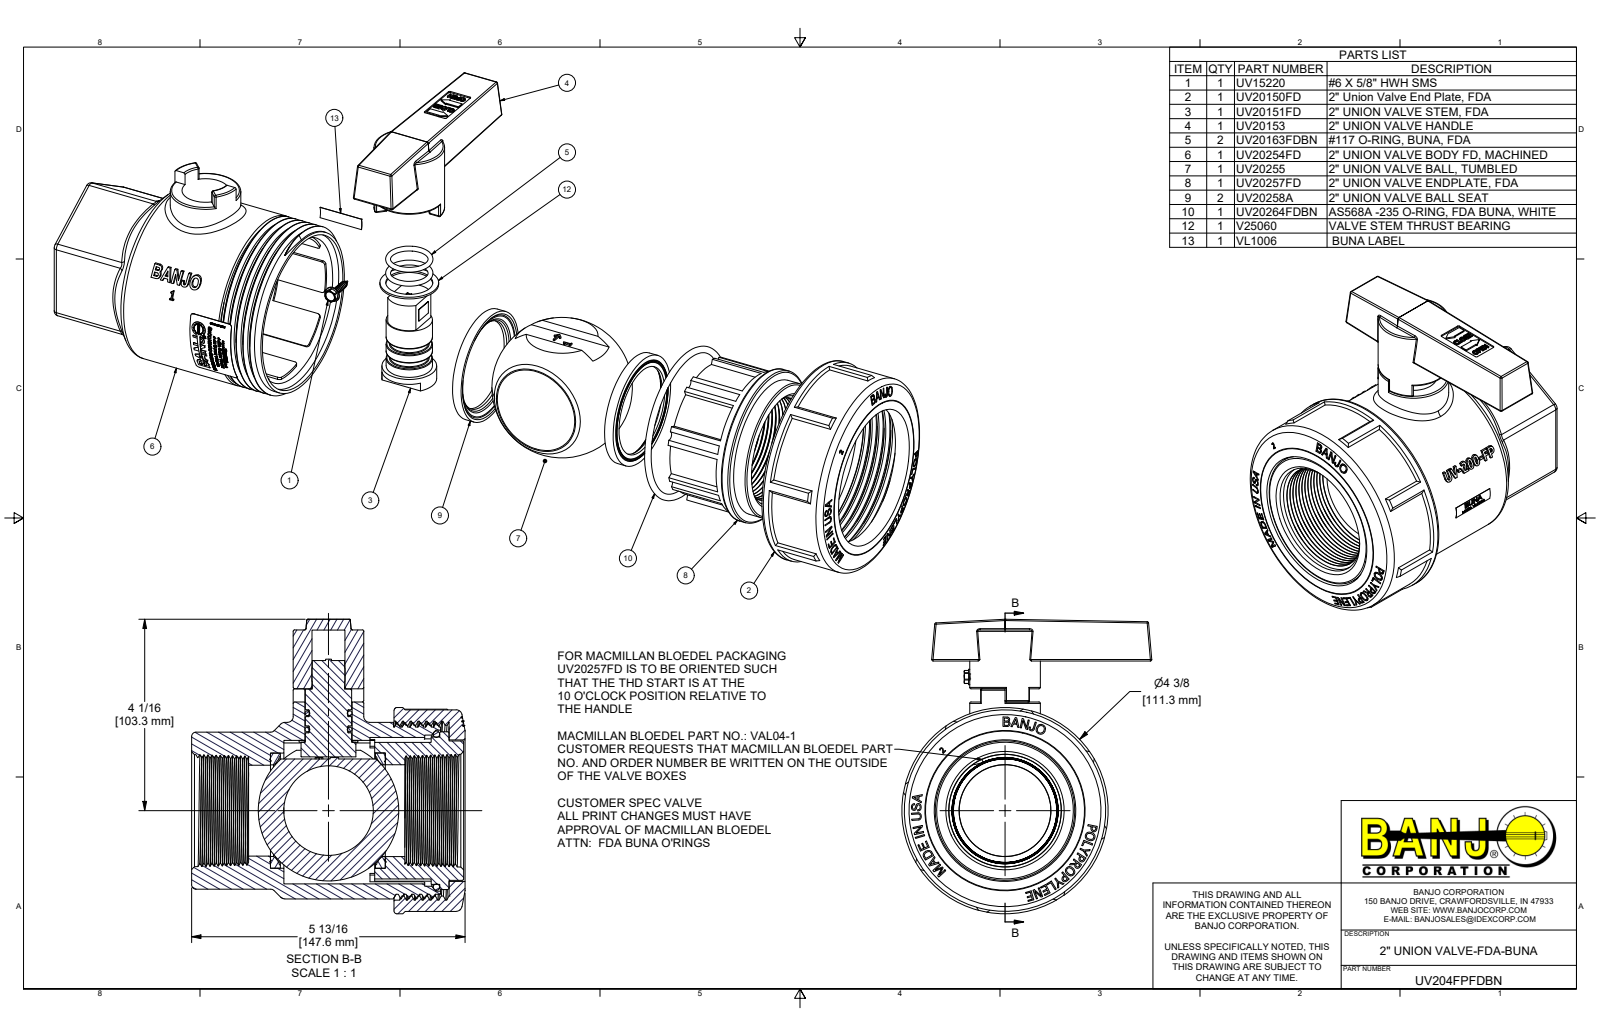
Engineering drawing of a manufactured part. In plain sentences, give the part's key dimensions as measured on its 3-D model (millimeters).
The part is named "UV204FPFDBN; UV20150FD; UV20151FD; UV20153 (+8 more)". Its 3-D file was written by "Autodesk Inventor 2022 (AUTOMOTIVE_DESIGN)". It is 15 solids with 3148 faces: 1516 planar, 444 cylindrical and 1188 other. Overall it measures 158.9 by 147.6 by 134.8 millimeters. Its volume is 689 400 cubic millimeters and its surface area 223 000 square millimeters. Round holes: 1 of diameter 3.8, 1 of diameter 25.4, 1 of diameter 25.5, 1 of diameter 48.3, 1 of diameter 49, 1 of diameter 49.4, 1 of diameter 49.5, 1 of diameter 62.3, 1 of diameter 76.3, 1 of diameter 79, 1 of diameter 81.5, 1 of diameter 86.9. Round bosses or shafts: 1 of diameter 111.3, 1 of diameter 108.7, 1 of diameter 95.3, 1 of diameter 95.1, 1 of diameter 90.2, 1 of diameter 85.1, 1 of diameter 79.5, 1 of diameter 75.2. Partial cylindrical surfaces (rounded edges, fillets, slot ends): 63 of radius 0.8, 16 of radius 1.5, 8 of radius 2.4, 6 of radius 2.3, 6 of radius 3.2, 1 of radius 3.5, 1 of radius 11.9, 1 of radius 12.1. The main face-to-face distances are 74.2, 4.8, 96.4, 62, 34.4, 66.7, 4.7, 29.7, 7.2, 54.7. The hole center spacings are 72.1.
